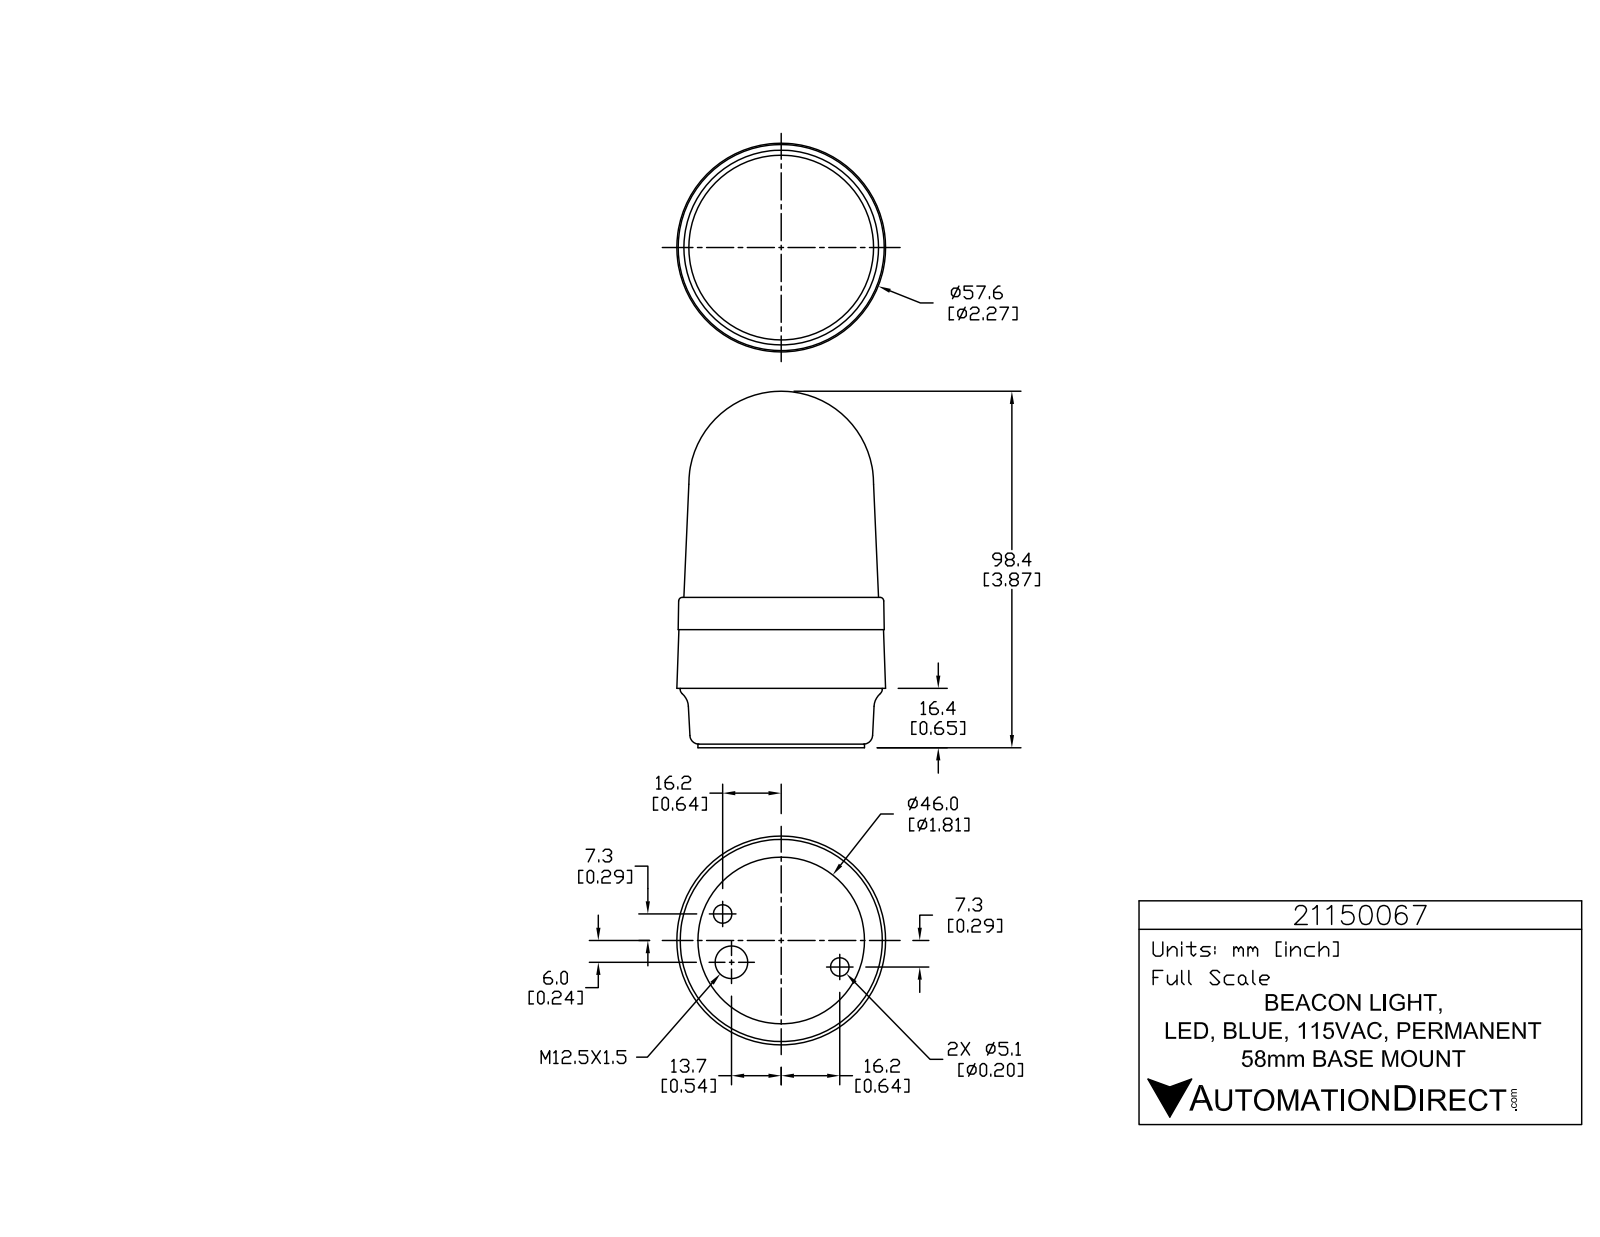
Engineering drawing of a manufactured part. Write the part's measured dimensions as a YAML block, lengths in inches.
part_name: "21150067"
step_written_by: "SolidWorks 2015 (AUTOMOTIVE_DESIGN)"
units: inches
bodies: {solids: 1, faces: 764, planar: 527, cylindrical: 145, other: 92}
overall_size: [3.874, 2.269, 2.269]
volume: 12.2
surface_area: 29.33
round_holes:
  - {diameter: 0.039, count: 3}
  - {diameter: 0.201, count: 2}
  - {diameter: 0.354, count: 1}
round_bosses_or_shafts:
  - {diameter: 0.226, count: 3}
  - {diameter: 0.056, count: 3}
  - {diameter: 2.197, count: 1}
  - {diameter: 1.811, count: 1}
partial_cylinders:
  - {radius: 0.008, count: 6}
  - {radius: 0.008, count: 6}
  - {radius: 0.008, count: 6}
  - {radius: 0.131, count: 6}
  - {radius: 0.004, count: 3}
  - {radius: 0.005, count: 3}
  - {radius: 0.007, count: 3}
  - {radius: 0.008, count: 3}
face_to_face_distances: [0.646, 0.039, 0.606, 1.634, 1.594, 0.988, 1.283, 1.244, 0.638, 0.35]
hole_center_spacings: [0.534, 1.179, 1.398]
